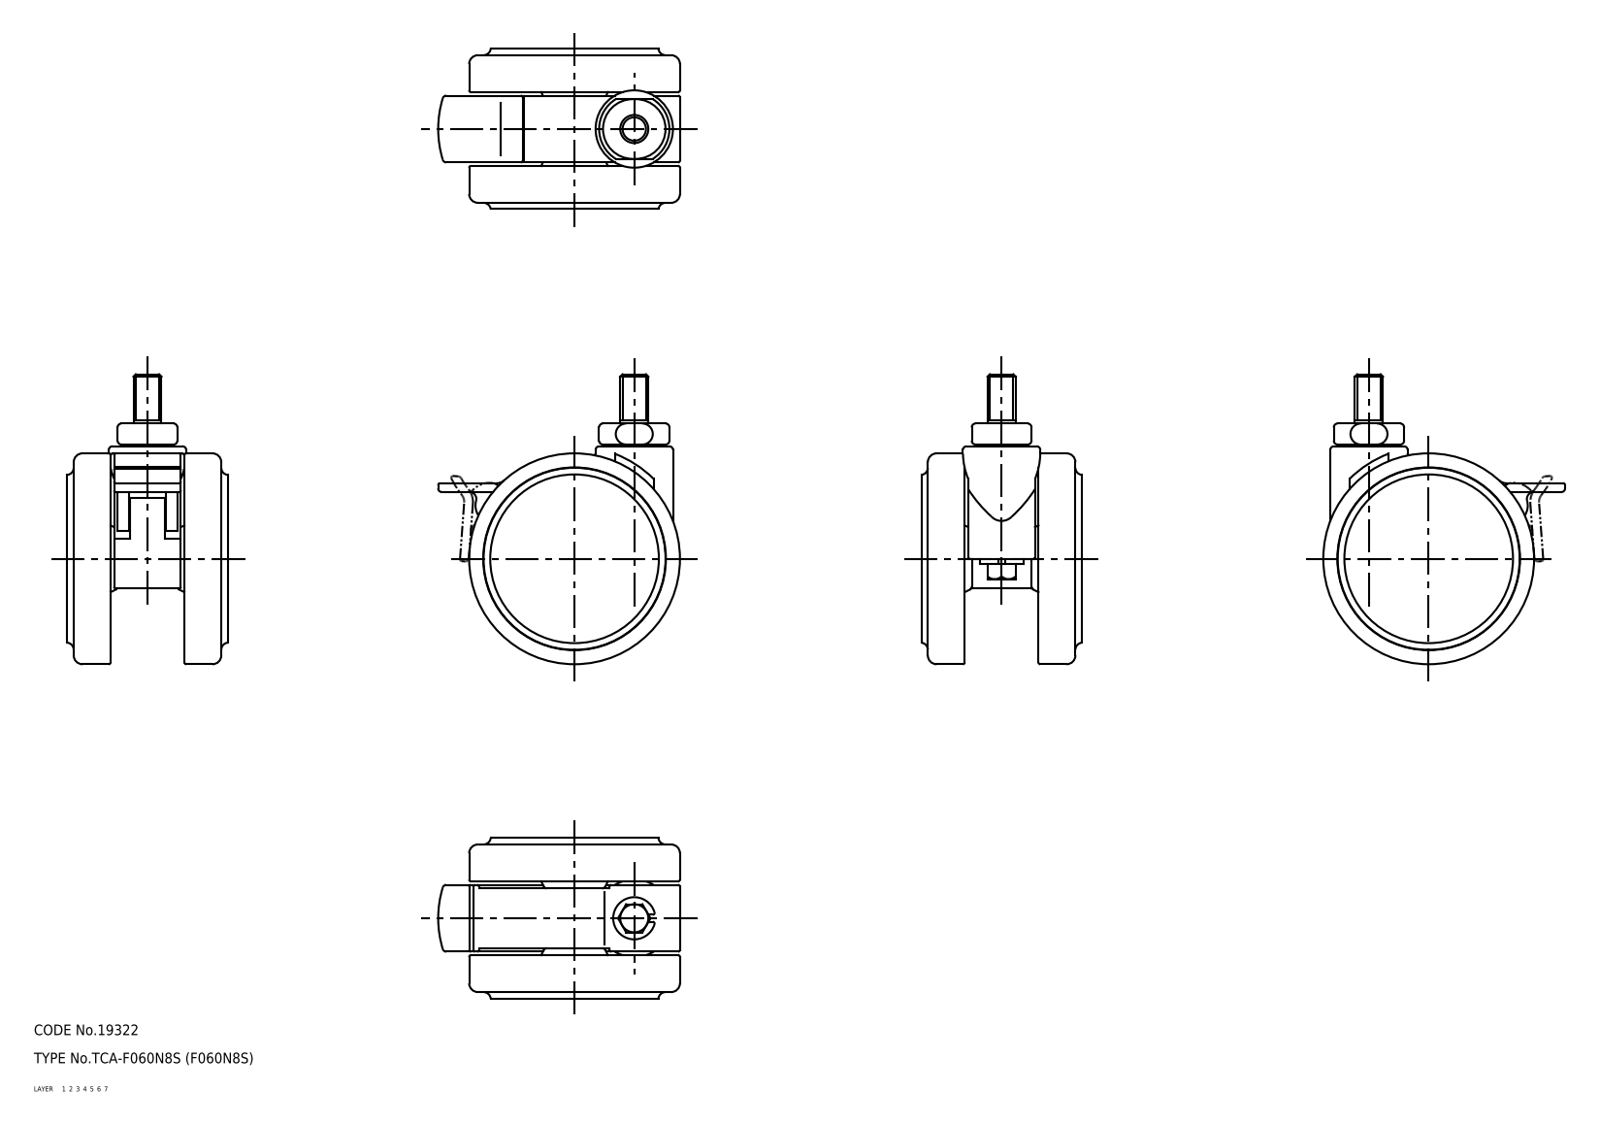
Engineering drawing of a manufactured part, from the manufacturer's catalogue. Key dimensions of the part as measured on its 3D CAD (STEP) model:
Part name (STEP PRODUCT): 67124951; 67124964; 67124977; 67124990 (+1 more)
STEP written by: CADfix (AUTOMOTIVE_DESIGN)
Units: millimetres
Bodies: 5 solids, 278 faces (0 planar, 0 cylindrical, 278 other)
Overall size (bounding box): 82.5 × 68.82 × 45.6
Volume: 82 402 mm³ · Surface area: 29 504 mm²
